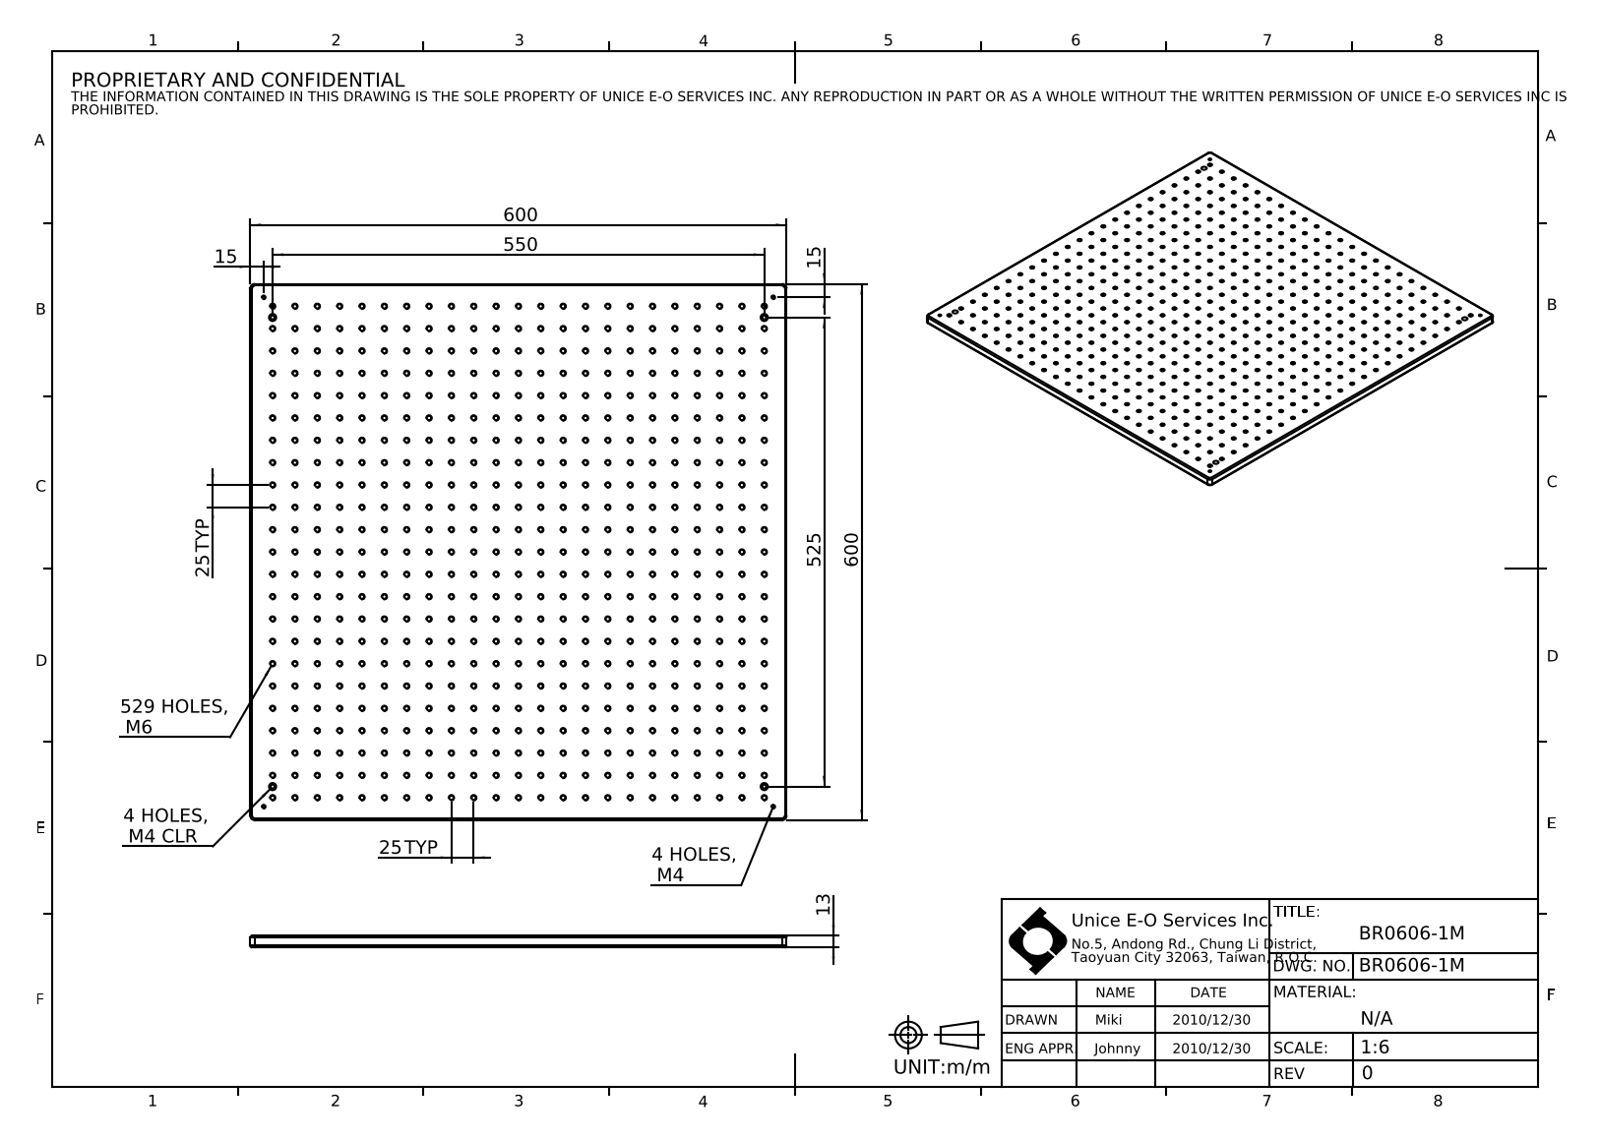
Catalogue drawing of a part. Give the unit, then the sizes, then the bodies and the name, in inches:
Units: inches
Overall size (bounding box): 23.622 × 23.622 × 0.512
Round holes (diameter × count): ⌀0.197 ×529, ⌀0.13 ×4, ⌀0.177 ×4, ⌀0.315 ×4
Partial cylindrical surfaces — rounded edges, fillets, slot ends (radius × count): R0.079 ×8, R0.197 ×4
Main face-to-face distances: 0.512, 23.622, 0.276, 0.236
Hole centre spacings: 0.984, 1.969, 2.953, 3.937, 4.921, 5.906, 6.89, 7.874
Volume: 276.9 in³ · Surface area: 1 295 in²
Bodies: 1 solid, 1112 faces (10 planar, 1094 cylindrical, 8 other)
Part name (STEP PRODUCT): BR0606-1M
STEP written by: SolidWorks 2016 (CONFIG_CONTROL_DESIGN)
